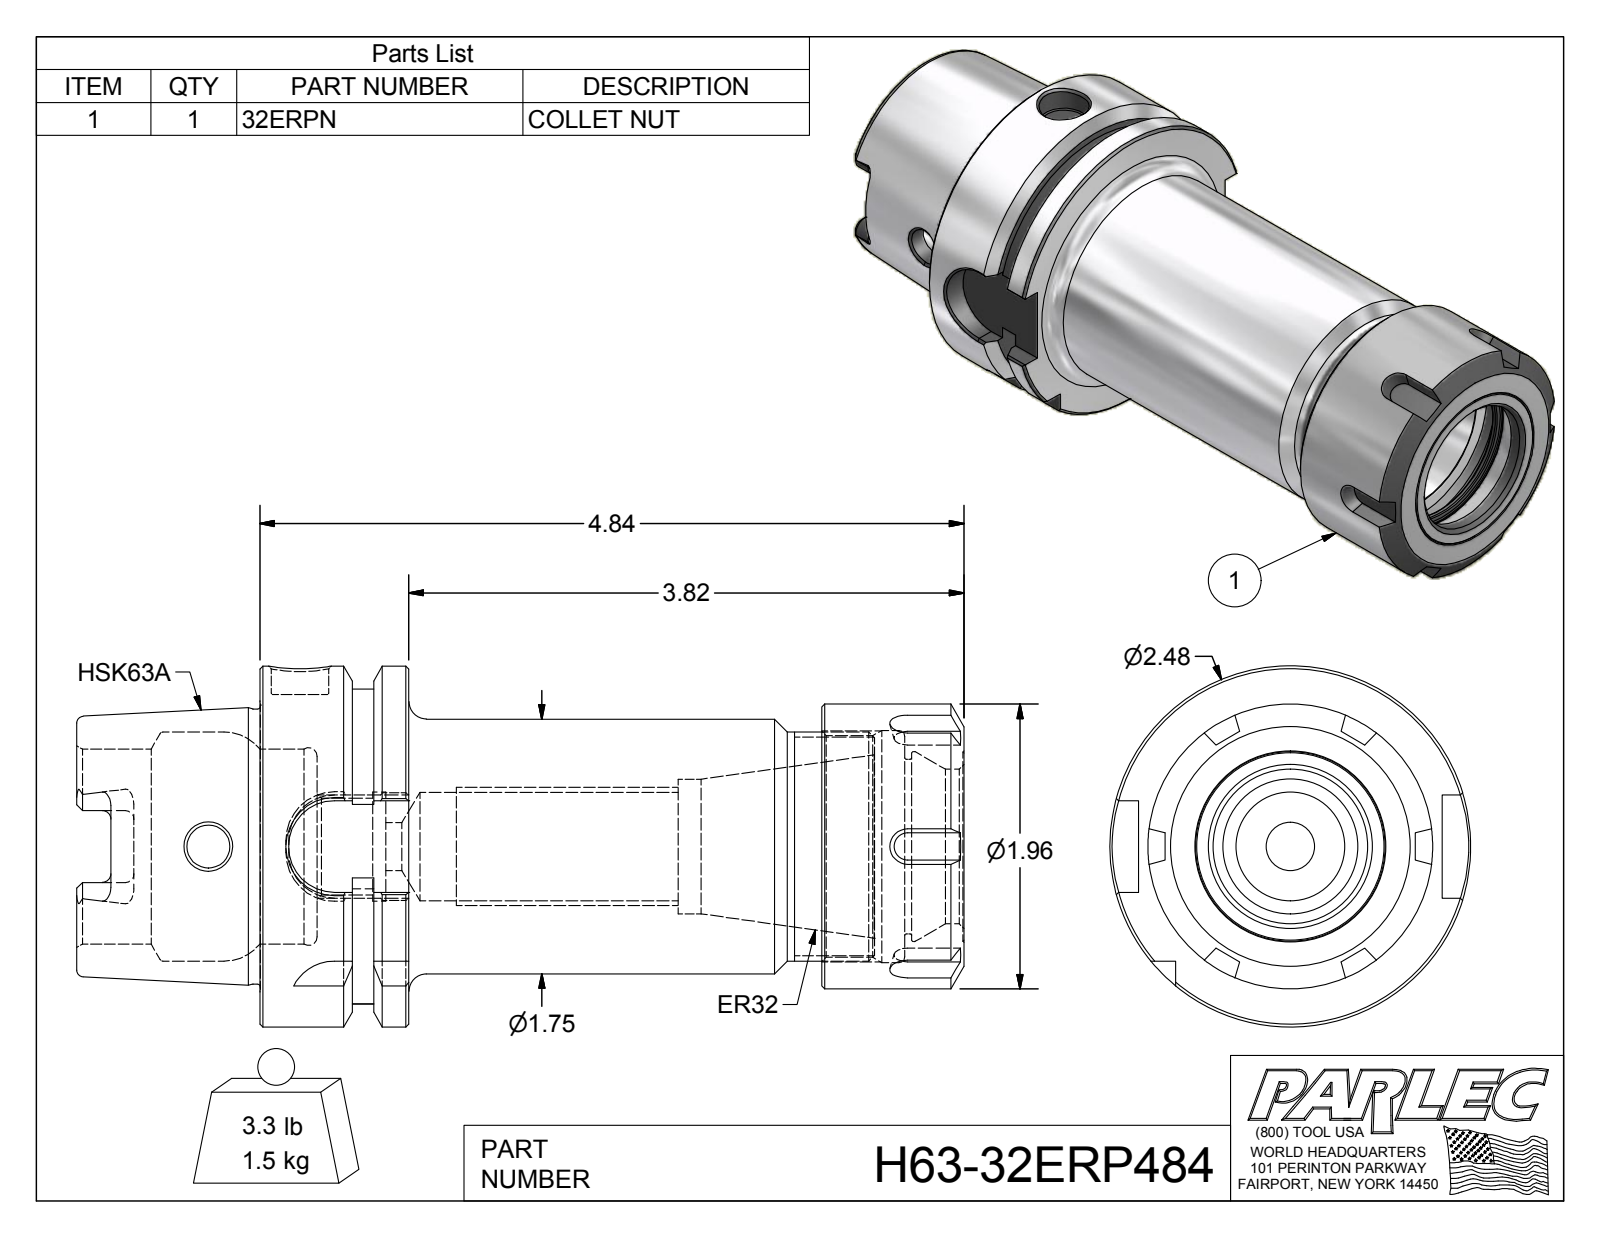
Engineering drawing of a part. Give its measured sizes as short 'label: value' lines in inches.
name: H63-32ERP484; H63-32ER5-1; 32ERPN
written by: Autodesk Inventor 2012 (AUTOMOTIVE_DESIGN)
unit: in
bodies: 2 solids, 186 faces (75 planar, 42 cylindrical, 69 other)
size: 6.1 × 2.48 × 2.48
volume: 11.67 in³; area: 74.16 in²
holes: 1× ⌀0.295, 1× ⌀0.331, 1× ⌀0.394, 1× ⌀0.666, 1× ⌀0.745, 1× ⌀0.749, 1× ⌀0.925, 1× ⌀1.063, 1× ⌀1.2, 1× ⌀1.305, 1× ⌀1.339, 1× ⌀1.523
bosses: 1× ⌀2.48, 1× ⌀1.958, 1× ⌀1.891, 1× ⌀1.75
rounds: 6× R0.059, 4× R0.113, 4× R0.315, 1× R1.083
face distances: 1.024, 4.84, 3.817, 3.862, 2.839, 0.978, 0.394, 0.63, 3.469, 4.446
